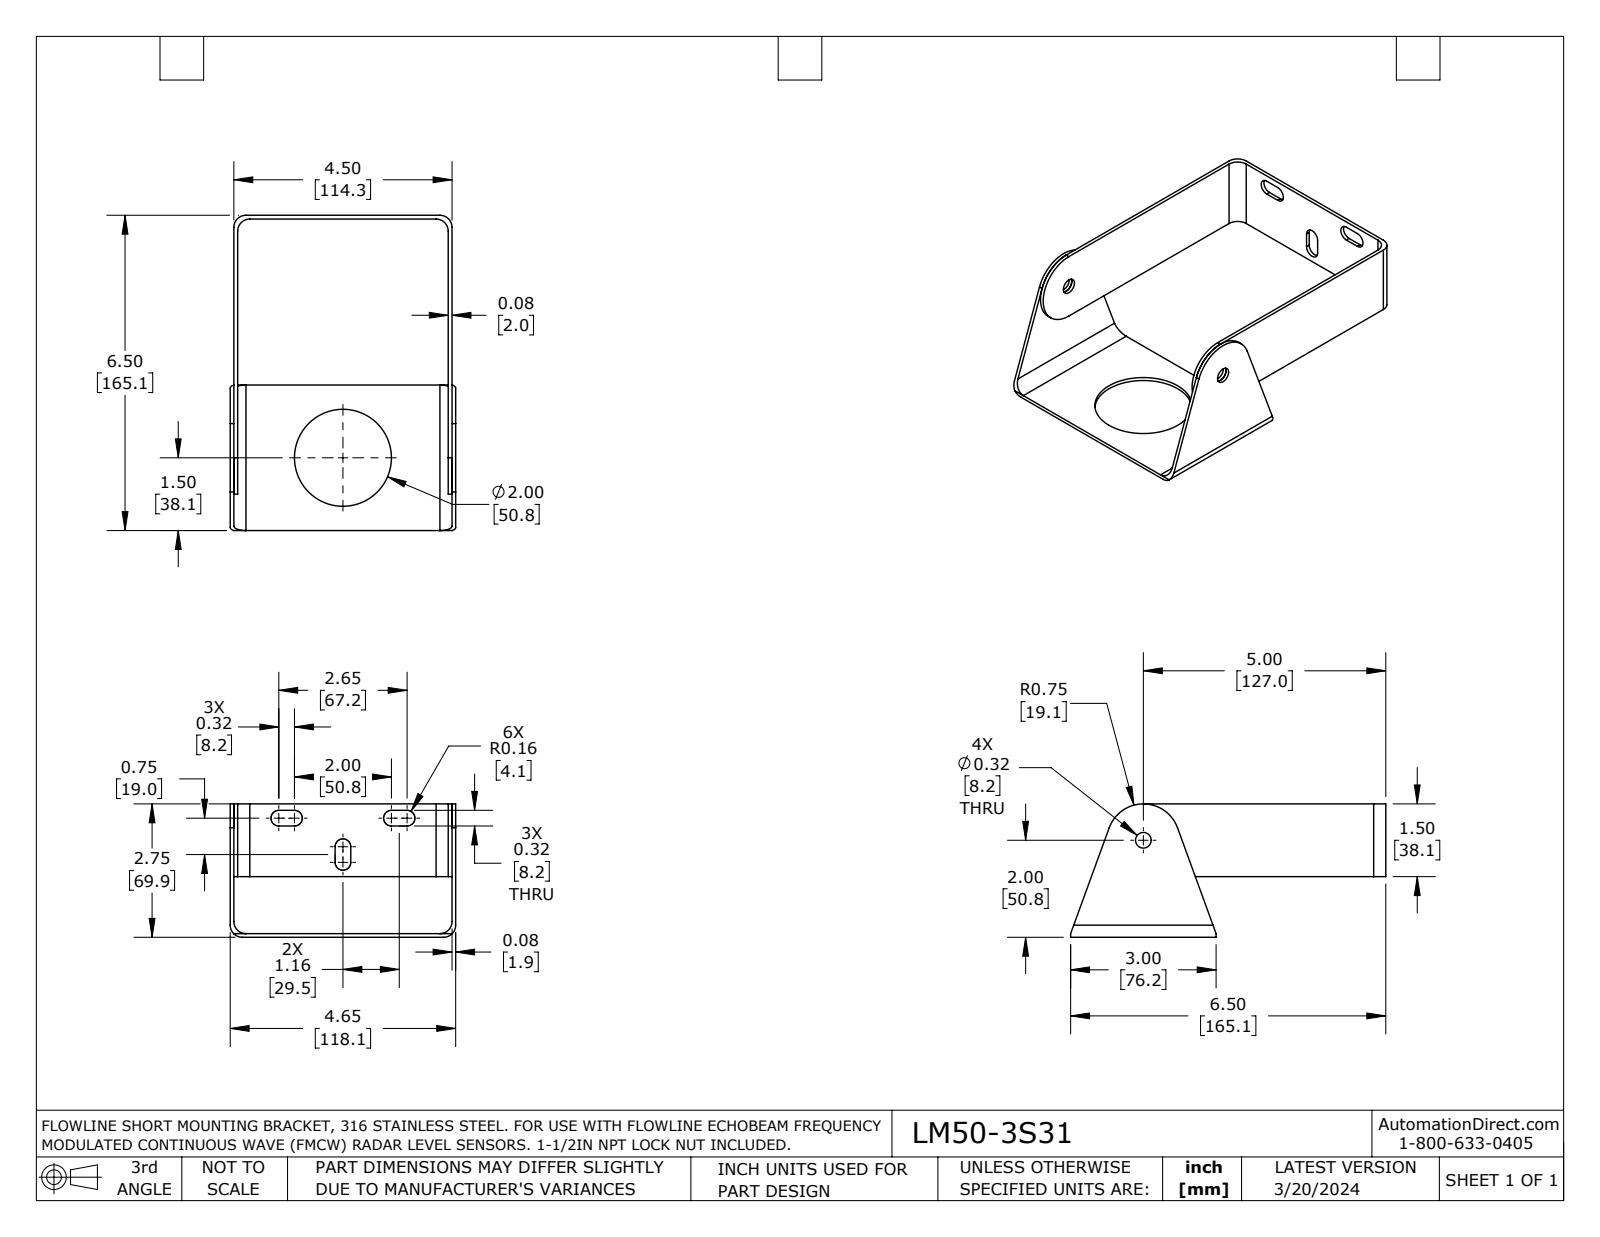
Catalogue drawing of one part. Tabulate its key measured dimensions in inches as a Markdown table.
| quantity | value |
| --- | --- |
| part name | LM50-3S31 |
| STEP written by | SolidWorks 2021 (AUTOMOTIVE_DESIGN) |
| units | inches |
| bodies | 2 solids, 57 faces (26 planar, 31 cylindrical, 0 other) |
| overall size | 6.5 × 4.65 × 2.75 |
| volume | 3.371 in³ |
| surface area | 91.21 in² |
| round holes (diameter × count) | 0.323 × 1, 2 × 1 |
| partial cylindrical surfaces (radius × count) | 0.25 × 8, 0.161 × 6, 0.75 × 1 |
| main face-to-face distances | 0.079, 0.075, 4.421, 4.5, 0.154, 4.496, 4.575, 4.343, 4.65, 2.75 |
